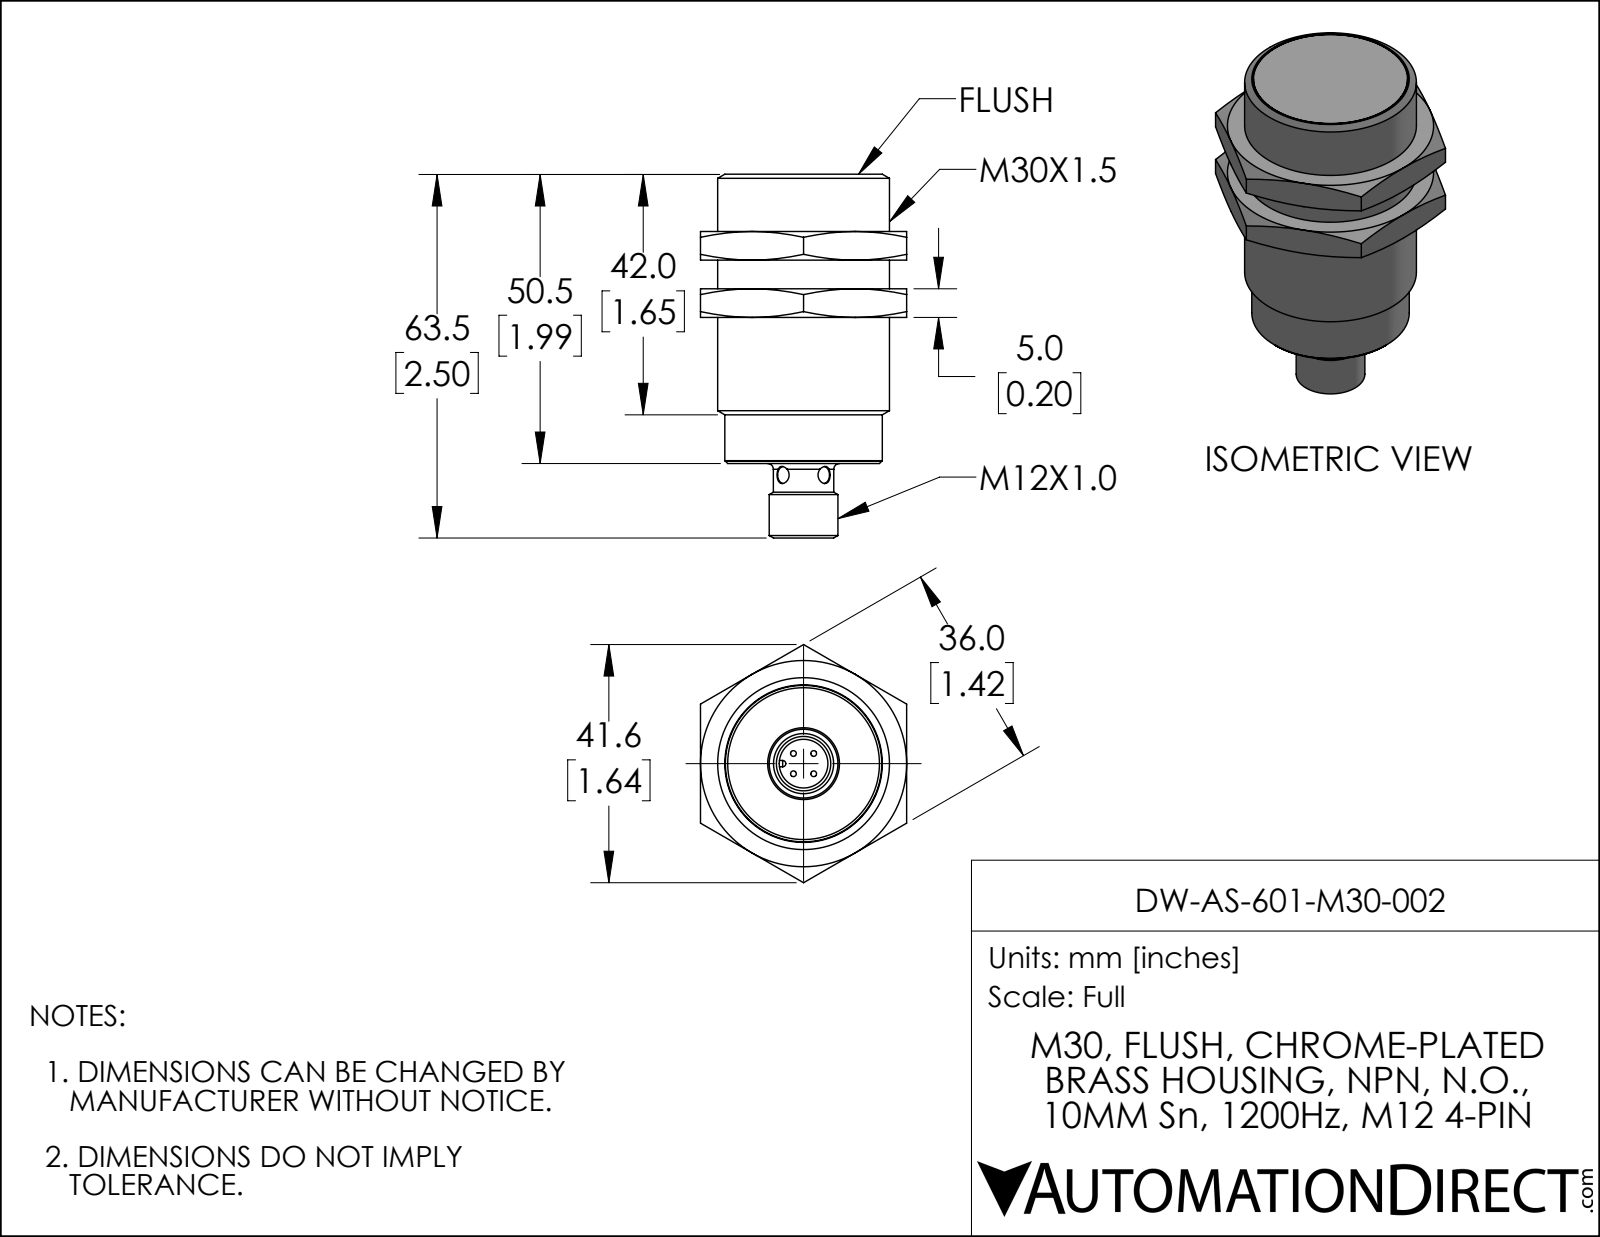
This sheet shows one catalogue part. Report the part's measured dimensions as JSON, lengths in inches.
{"part_name": "DW-AS-601-M30-002", "step_written_by": "SolidWorks 2019 (AUTOMOTIVE_DESIGN)", "units": "inches", "bodies": {"solids": 1, "faces": 85, "planar": 29, "cylindrical": 20, "other": 36}, "overall_size": [2.5, 1.637, 1.417], "volume_in3": 2.412, "surface_area_in2": 13.37, "round_holes": [[0.118, 2], [0.335, 1], [1.068, 1]], "round_bosses_or_shafts": [[0.039, 4], [1.181, 1], [1.083, 1], [1.075, 1], [1.059, 1], [0.472, 1], [0.415, 1]], "partial_cylinders_radius": [[0.022, 2]], "face_to_face_distances": [0.394, 0.197, 0.591, 1.417, 1.988, 0.984, 0.787, 1.594, 1.201, 1.004]}
